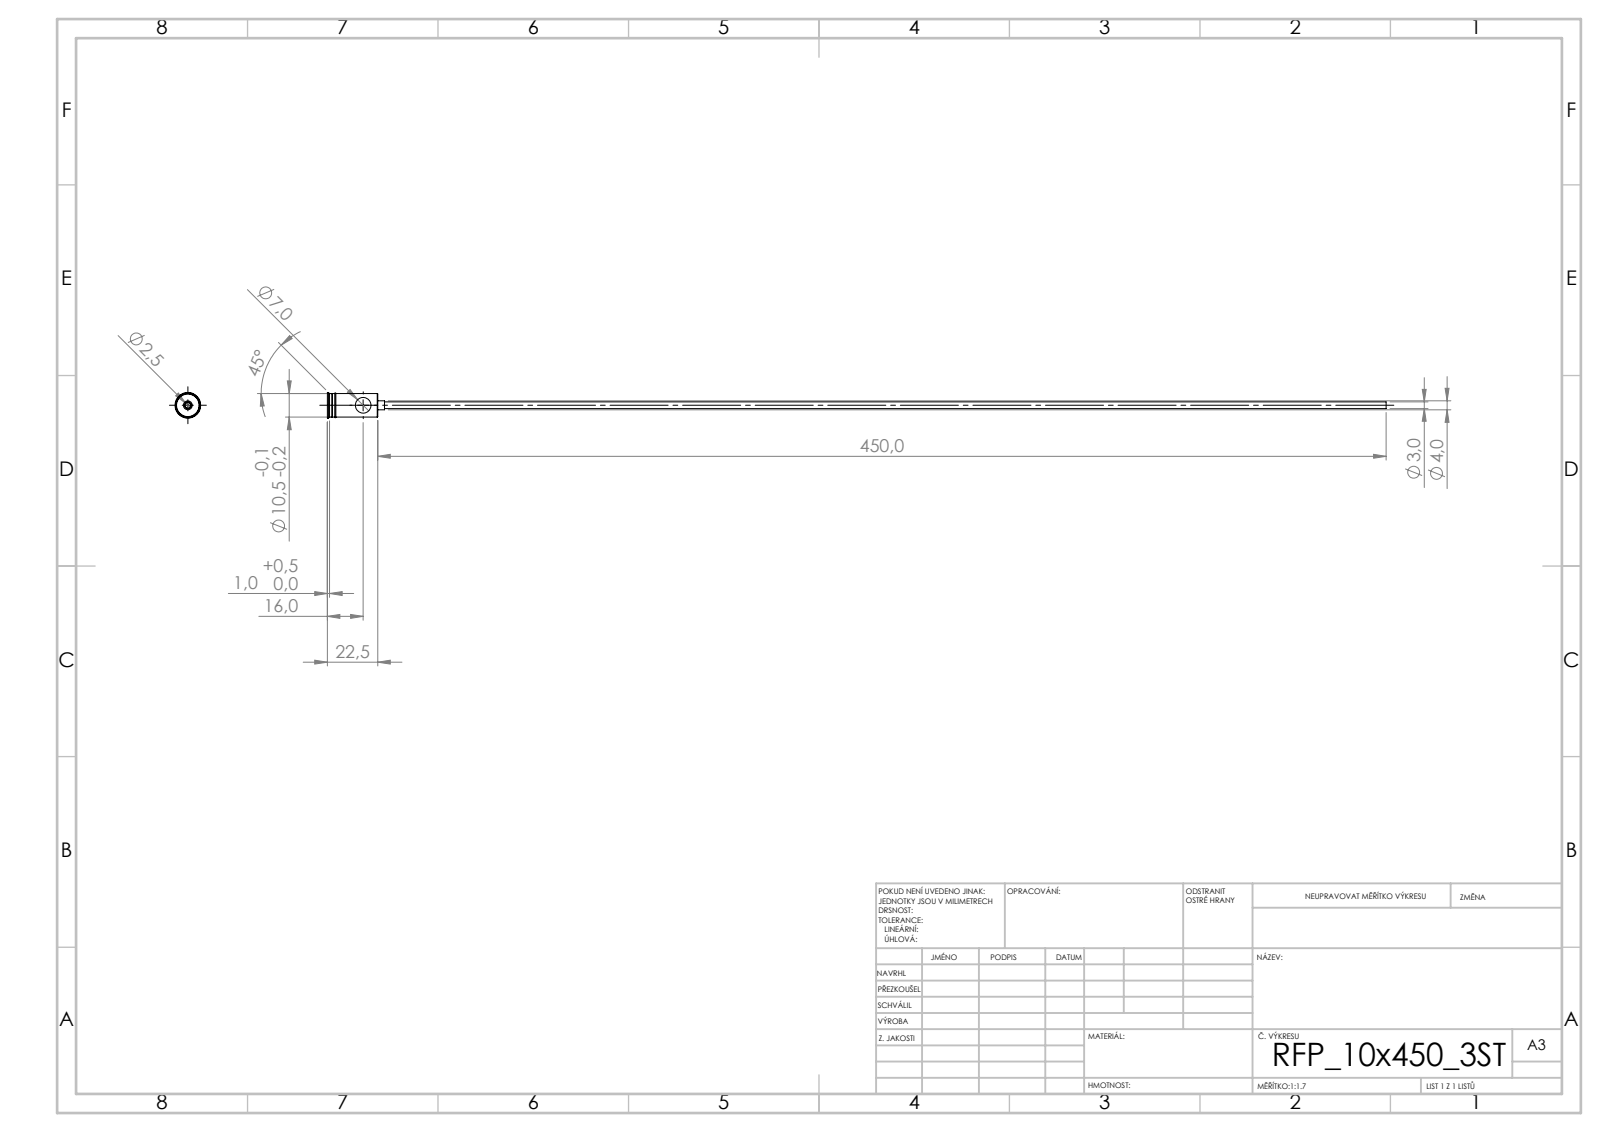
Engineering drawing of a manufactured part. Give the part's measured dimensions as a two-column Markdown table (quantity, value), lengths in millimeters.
| quantity | value |
| --- | --- |
| STEP written by | SolidWorks 2019 (CONFIG_CONTROL_DESIGN) |
| units | millimeters |
| bodies | 1 solid, 44 faces (20 planar, 16 cylindrical, 8 other) |
| overall size | 472.5 × 11.5 × 11.5 |
| volume | 2 496 mm³ |
| surface area | 8 924 mm² |
| round holes (diameter × count) | 2.5 × 1, 7 × 1 |
| round bosses / shafts (diameter × count) | 11.5 × 1, 10.5 × 1, 4 × 1, 3 × 1 |
| main face-to-face distances | 22.5, 20.5, 2, 5.9, 20.2, 2.3, 3, 23.2, 23.5, 25.5 |
